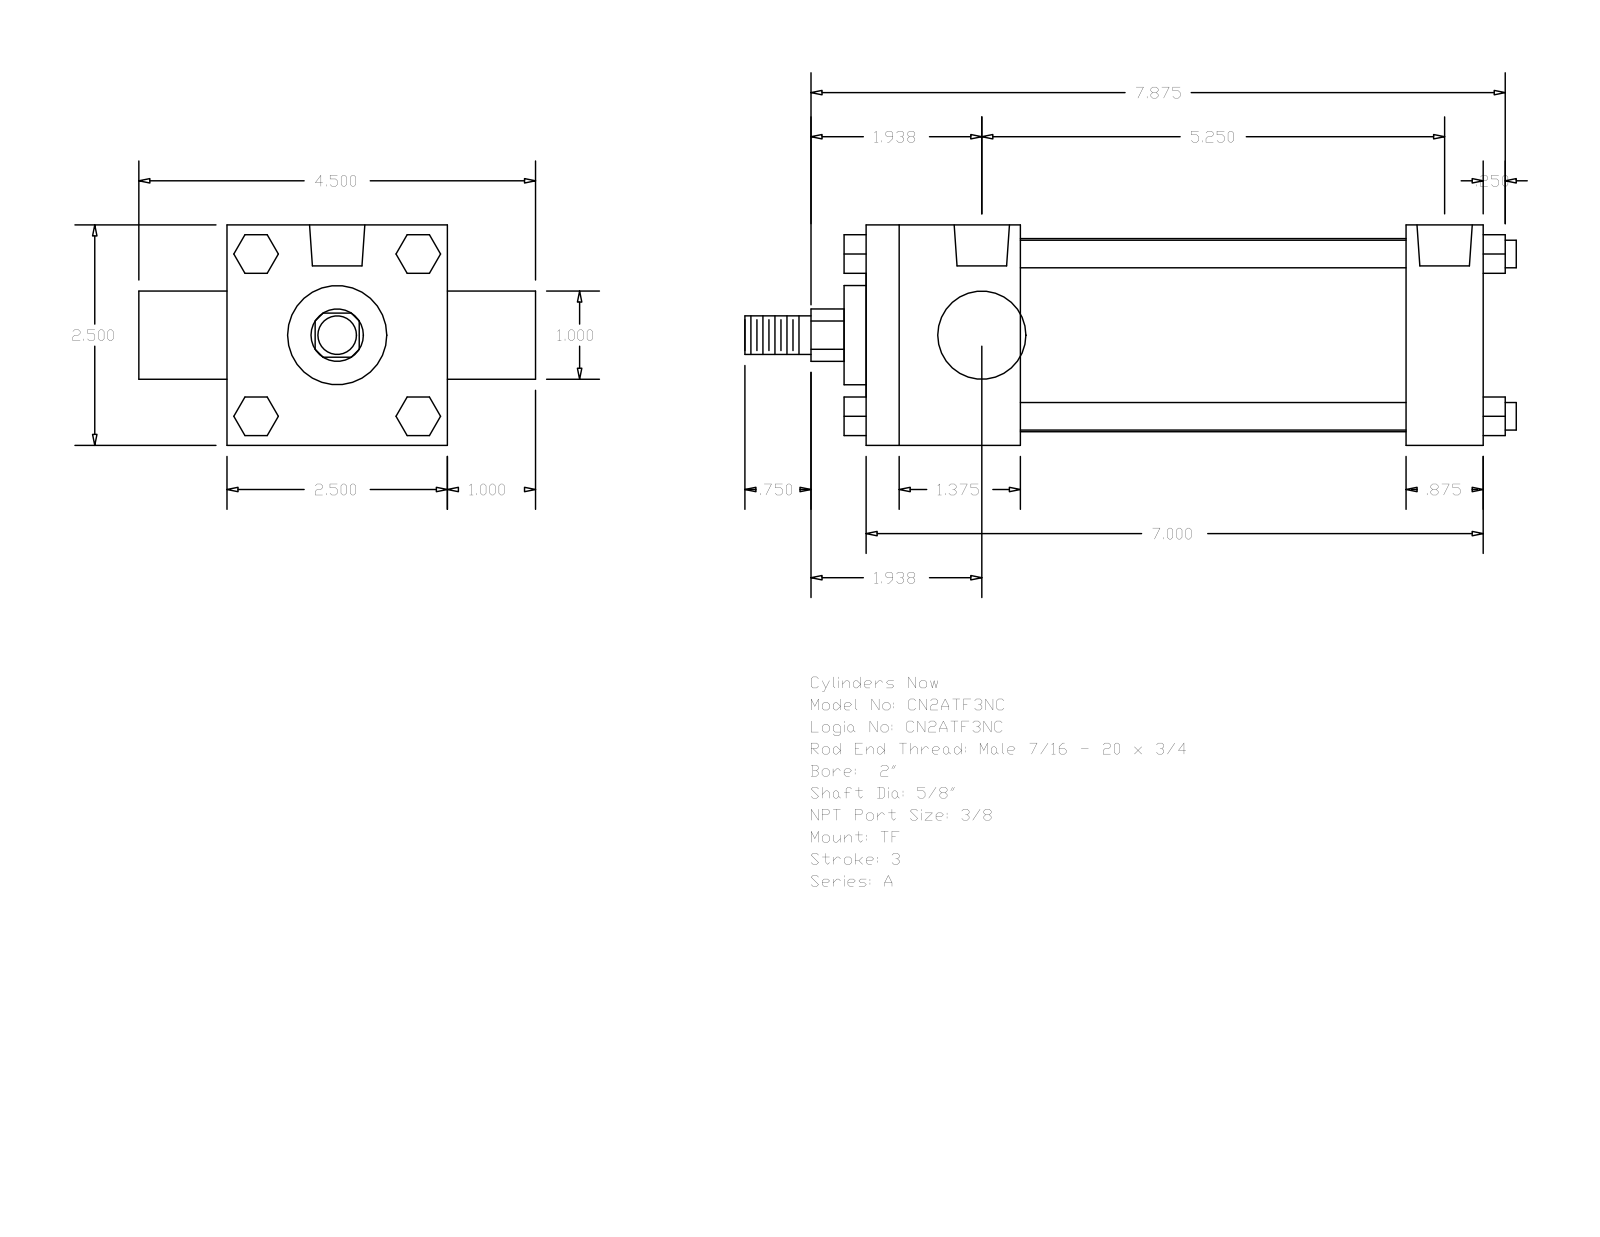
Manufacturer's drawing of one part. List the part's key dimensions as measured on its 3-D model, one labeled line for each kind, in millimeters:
Part name (STEP PRODUCT): A_TF__0200_0.625
STEP written by: GSSL Pune (CONFIG_CONTROL_DESIGN)
Units: millimetres
Bodies: 0 solids, 120 faces (92 planar, 28 cylindrical, 0 other)
Overall size (bounding box): 222.25 × 114.3 × 63.5
Round holes (diameter × count): ⌀5.56 ×3, ⌀15.93 ×2
Round bosses / shafts (diameter × count): ⌀7.94 ×4, ⌀55.63 ×1, ⌀28.57 ×1, ⌀25.4 ×1, ⌀15.88 ×1, ⌀11.11 ×1
Partial cylindrical surfaces — rounded edges, fillets, slot ends (radius × count): R7.54 ×1
Main face-to-face distances: 63.5, 177.8, 44.45, 155.57, 111.12, 133.35, 22.23, 25.4, 88.9, 6.35
Hole centre spacings: 3.97, 3.98, 125.4, 129.37, 129.38, 133.35
